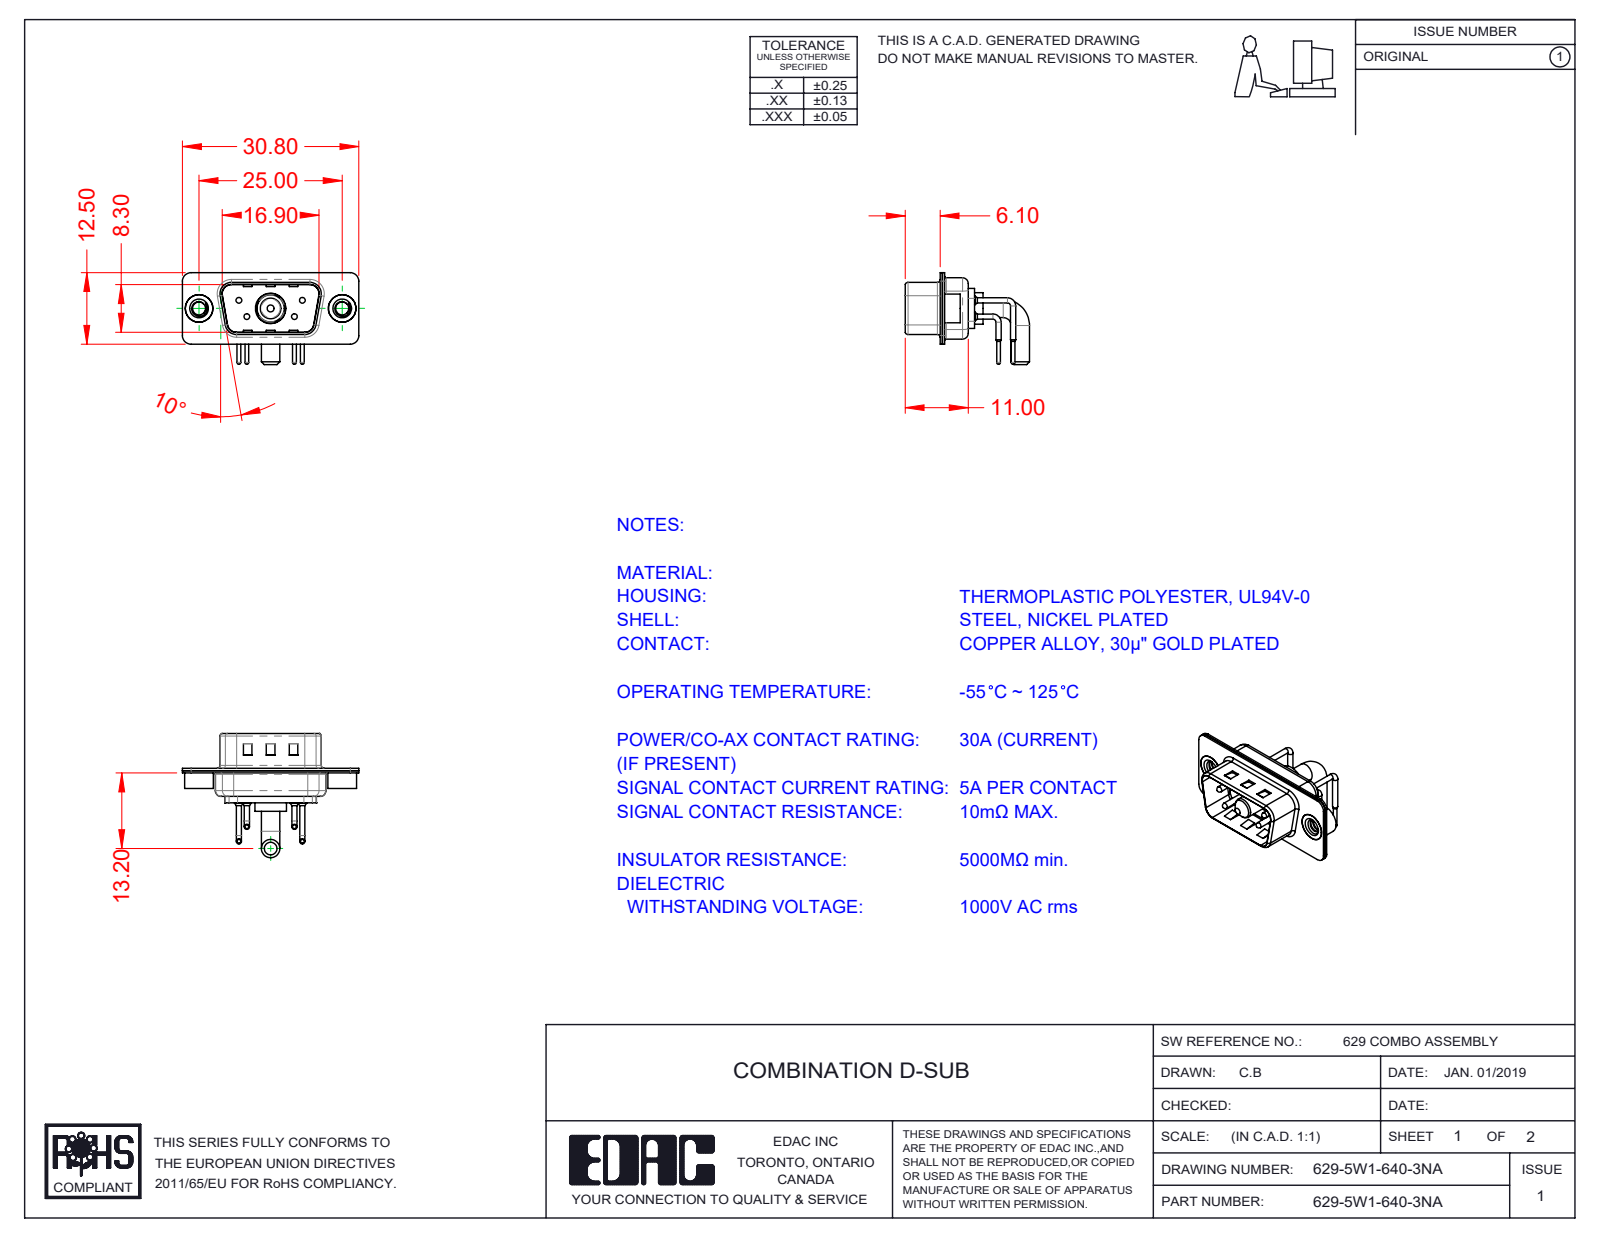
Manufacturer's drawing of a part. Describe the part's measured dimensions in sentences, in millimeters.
The part is named "629-5W1-640-3NA; 629Combo Shell Rear_09 Contacts; 629Combo Contact Row 2; 629Combo Shell Front_09 Contacts (+4 more)". Its 3-D file was written by "SolidWorks 2020 (CONFIG_CONTROL_DESIGN)". It is 11 solids with 787 faces: 373 planar, 294 cylindrical and 120 other. Overall it measures 30.8 by 21.7 by 16.05 millimeters. Its volume is 1 506 cubic millimeters and its surface area 3 790 square millimeters. Round holes: 4 of diameter 0.75, 4 of diameter 1.6, 4 of diameter 2, 2 of diameter 2.26, 2 of diameter 4, 2 of diameter 4.8, 1 of diameter 4.85, 1 of diameter 5.3. Round bosses or shafts: 8 of diameter 0.9, 4 of diameter 1.5, 4 of diameter 1, 4 of diameter 0.65, 2 of diameter 5, 2 of diameter 4.9, 2 of diameter 3.2, 1 of diameter 5.5. Partial cylindrical surfaces (rounded edges, fillets, slot ends): 16 of radius 1.5, 12 of radius 2, 8 of radius 0.5, 8 of radius 1.6, 4 of radius 0.25, 4 of radius 0.6, 4 of radius 0.65, 4 of radius 0.9. The main face-to-face distances are 0.4, 0.8, 9.5, 9.1, 8.7, 9.9, 0.65, 5.6, 1.2, 0.75. The hole center spacings are 3.16, 5.72, 7.1, 12.5, 18.1, 4.39, 4.4, 8.31.
